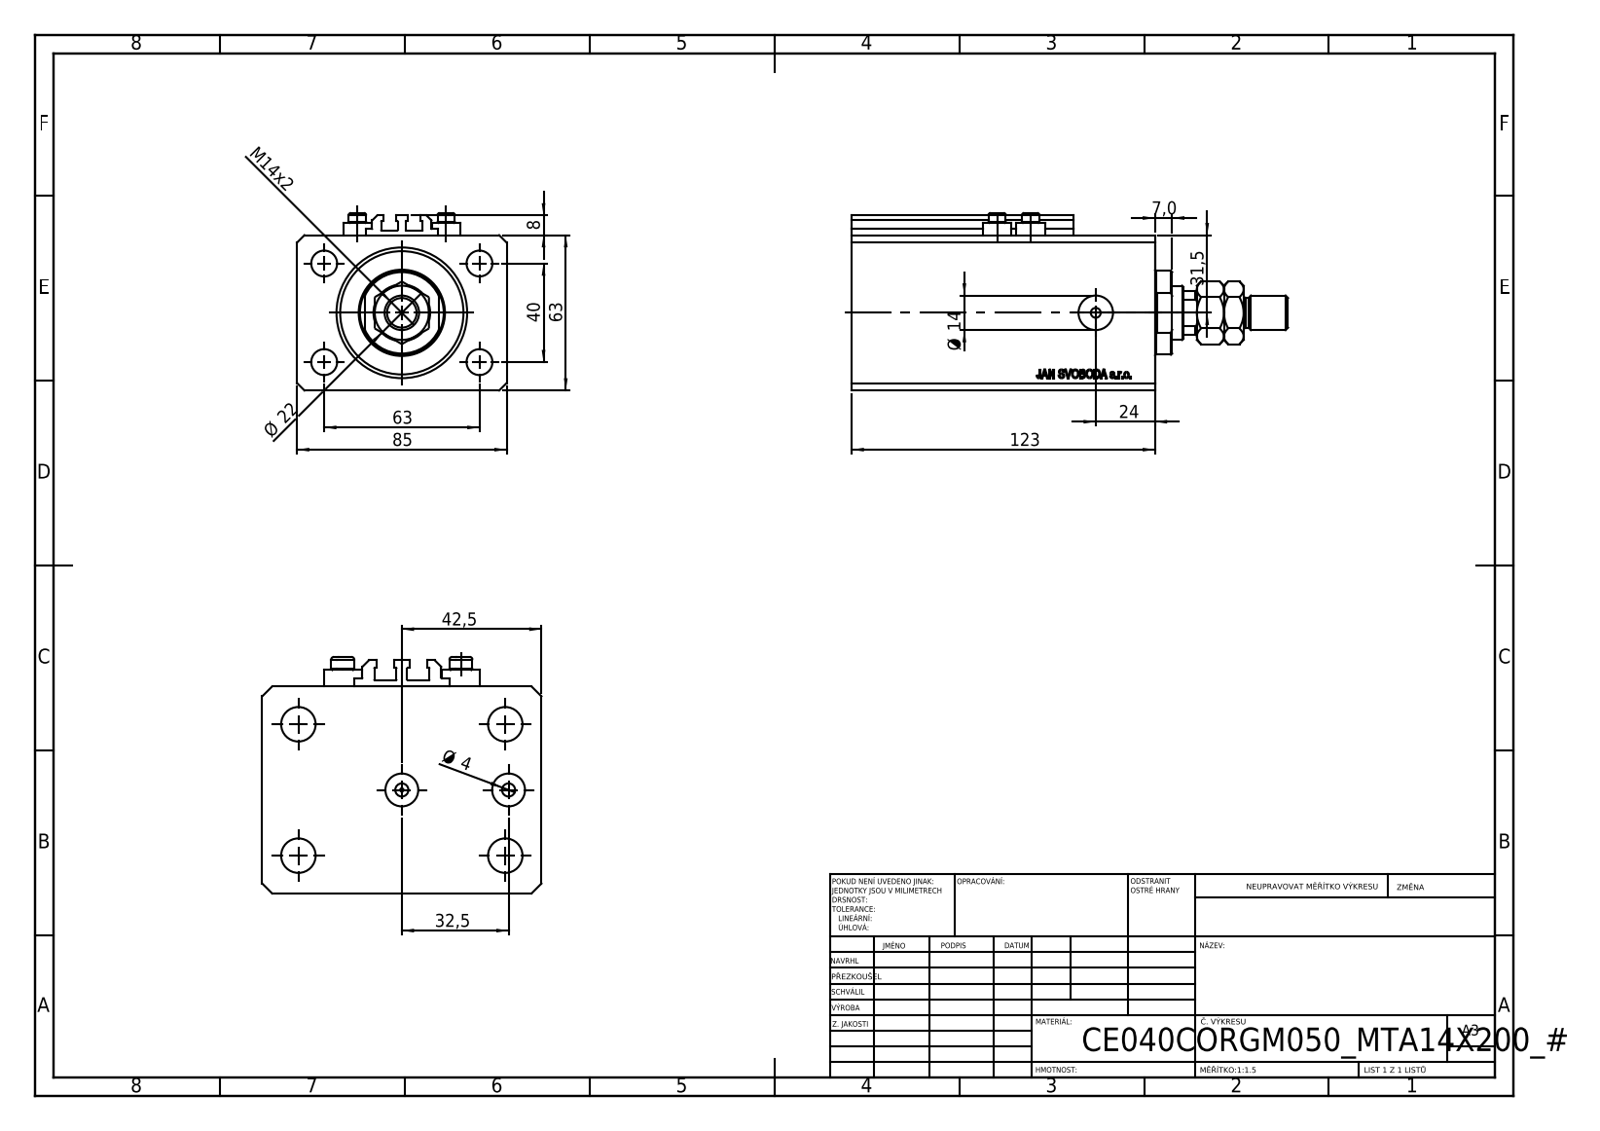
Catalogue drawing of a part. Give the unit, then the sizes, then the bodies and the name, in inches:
Units: inches
Overall size (bounding box): 6.969 × 3.346 × 2.835
Round holes (diameter × count): ⌀0.157 ×8, ⌀0.413 ×4, ⌀0.394 ×2, ⌀0.551 ×2, ⌀0.049 ×1, ⌀0.492 ×1, ⌀0.866 ×1, ⌀1.575 ×1, ⌀2.087 ×1
Round bosses / shafts (diameter × count): ⌀0.457 ×4, ⌀0.276 ×4, ⌀1.339 ×1, ⌀0.551 ×1, ⌀0.472 ×1
Partial cylindrical surfaces — rounded edges, fillets, slot ends (radius × count): R0.008 ×10, R0.413 ×1
Main face-to-face distances: 2.48, 3.346, 4.843, 0.669, 4.173, 0.449, 3.724, 4.394, 0.394, 0.098
Hole centre spacings: 1.469, 0.535, 0.788, 1.417, 1.515, 1.575, 2.48, 2.64
Volume: 36.46 in³ · Surface area: 181.7 in²
Bodies: 9 solids, 1087 faces (519 planar, 92 cylindrical, 476 other)
Part name (STEP PRODUCT): V250CE_VC_C; V250CE_C_VCP; MTA; V250CE_C_Body (+1 more)
STEP written by: SolidWorks 2019 (CONFIG_CONTROL_DESIGN)
